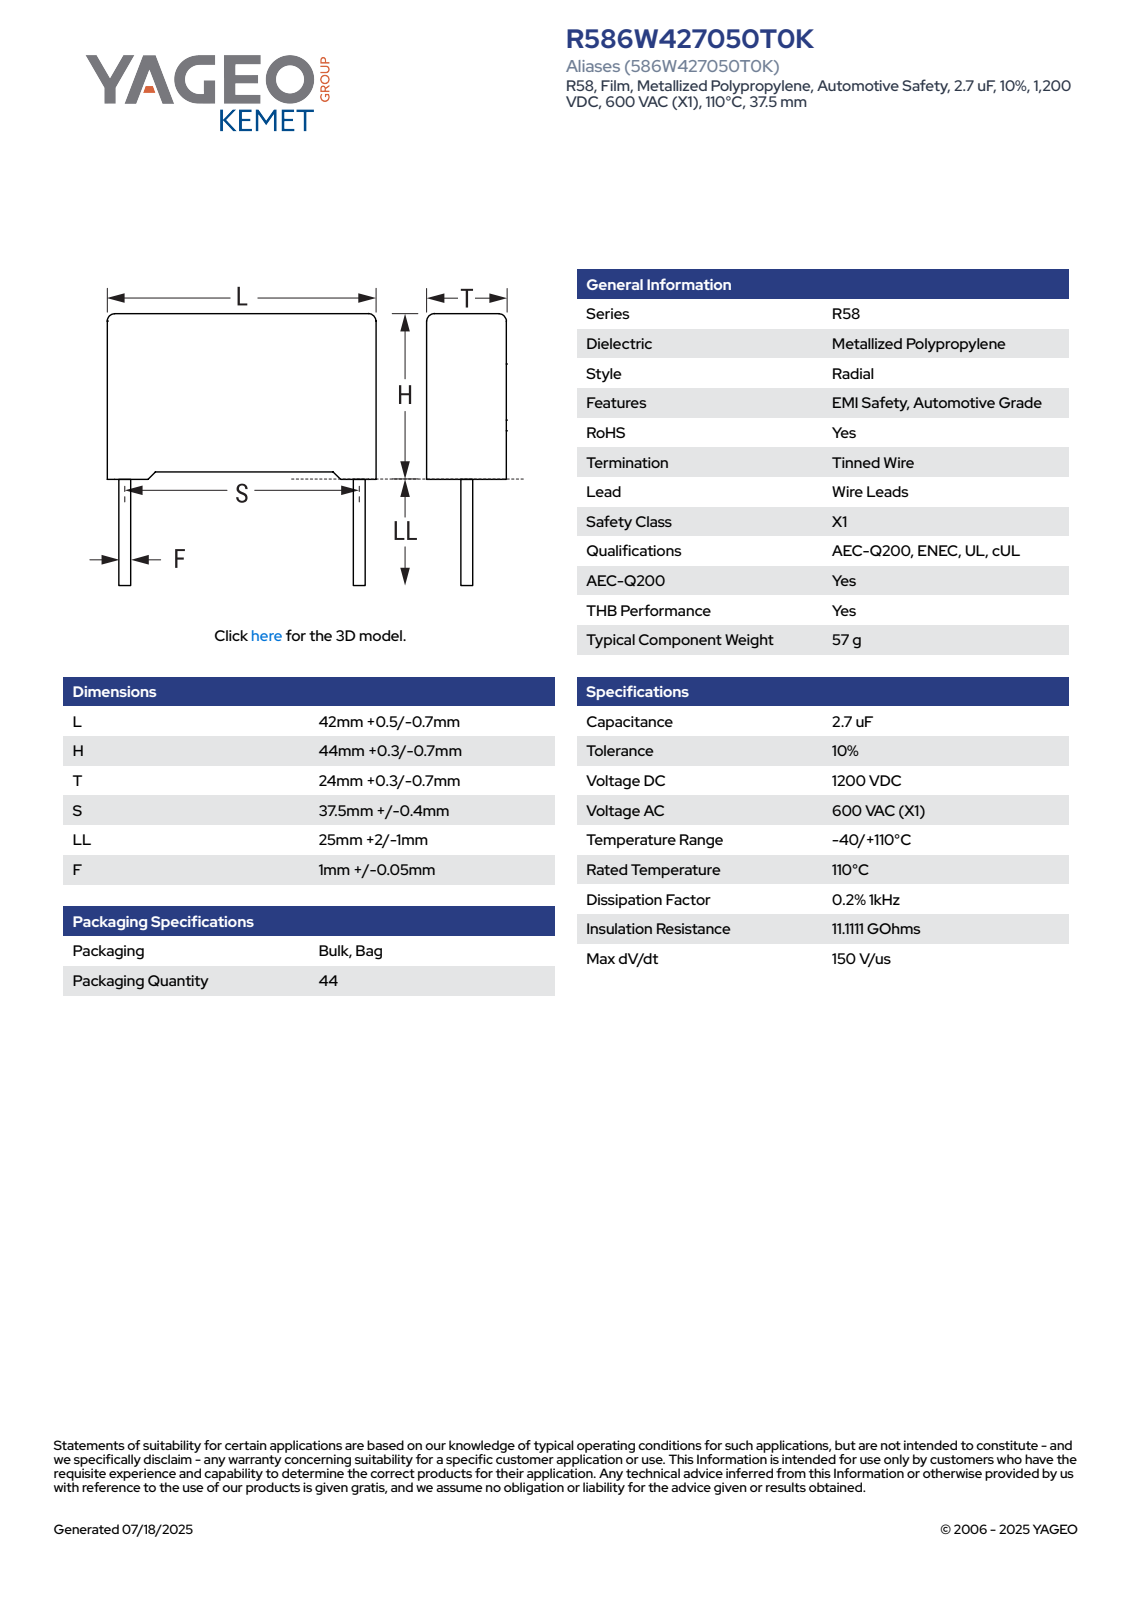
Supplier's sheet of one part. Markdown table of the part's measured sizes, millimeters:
| quantity | value |
| --- | --- |
| part name | CFR_RB2_42X44X24_L42.5H44.3T24.3S37.5LL27F1.05 |
| STEP written by | SolidWorks 2021 (AUTOMOTIVE_DESIGN) |
| units | millimeters |
| bodies | 4 solids, 85 faces (77 planar, 8 cylindrical, 0 other) |
| overall size | 71.3 × 42.5 × 24.3 |
| volume | 44 463 mm³ |
| surface area | 8 233 mm² |
| round bosses / shafts (diameter × count) | 1.05 × 2 |
| partial cylindrical surfaces (radius × count) | 0.5 × 4 |
| main face-to-face distances | 24.3, 42.5, 42.77, 0.78, 43.55, 0.75, 1.53, 44.3, 1.42, 24.31 |
